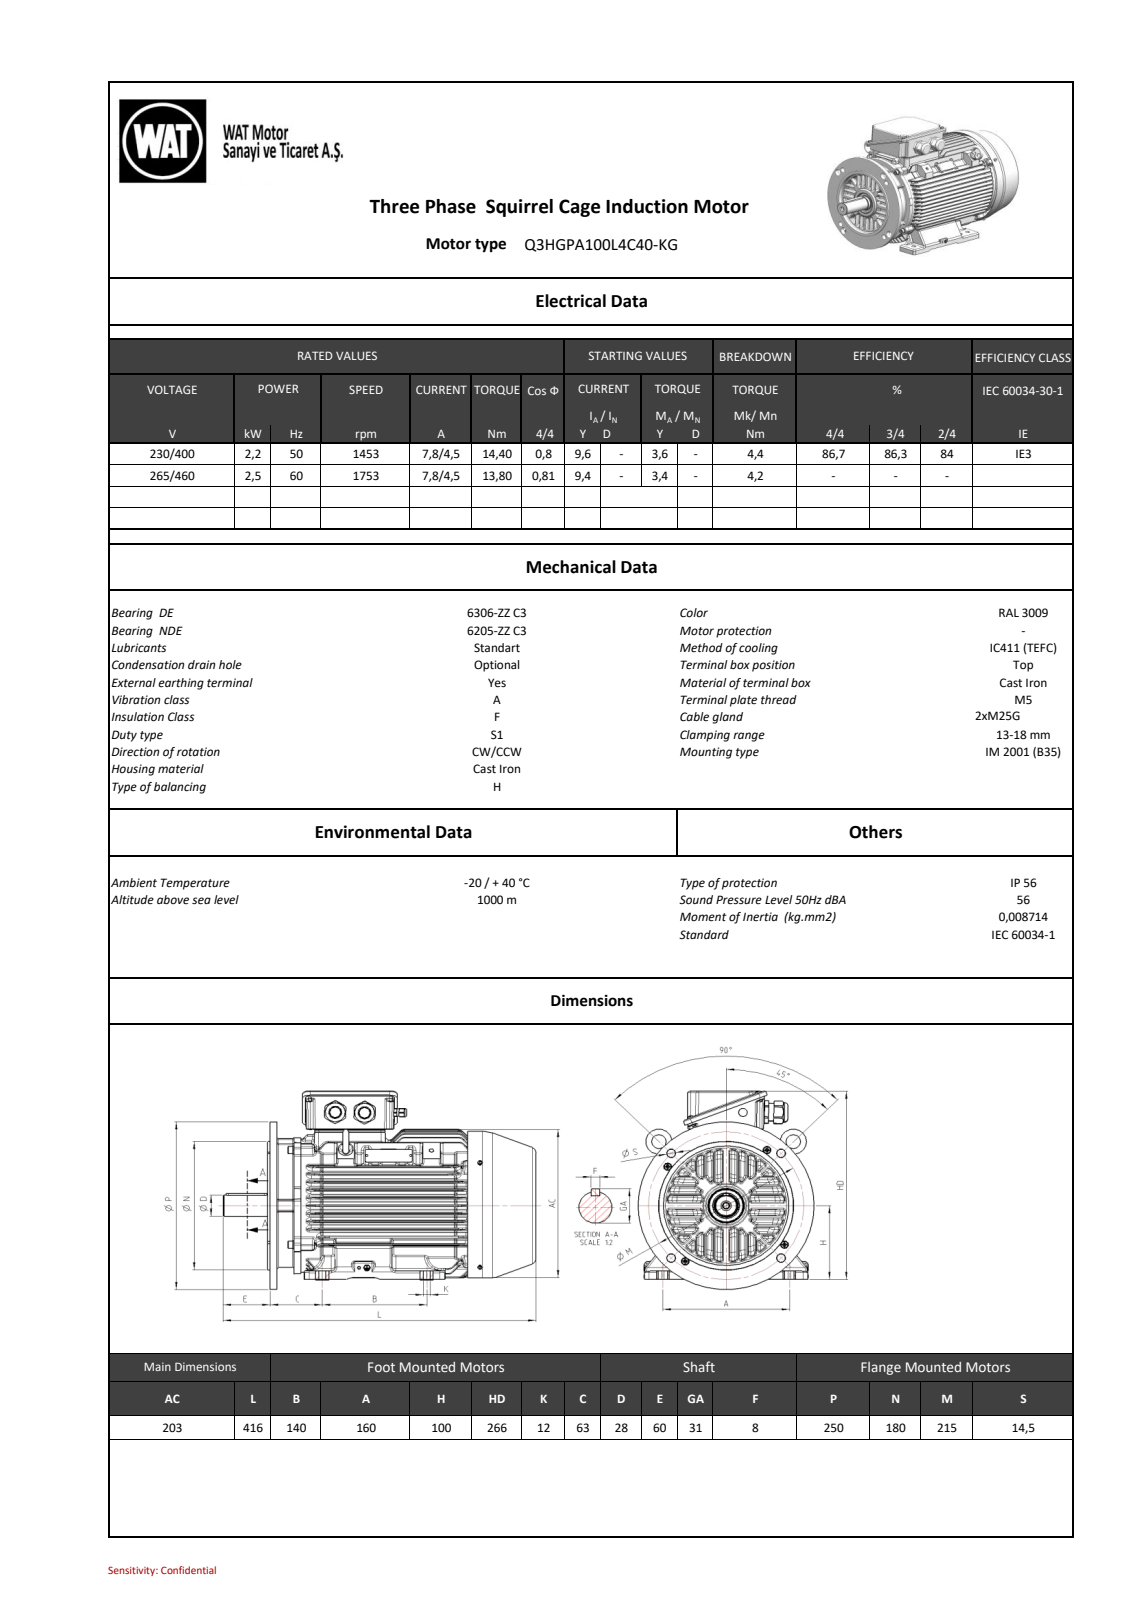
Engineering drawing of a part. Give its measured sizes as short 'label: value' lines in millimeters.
name: 26000A30F4D8roey
written by: SIEMENS PLM Software NX 11.0 (AUTOMOTIVE_DESIGN)
unit: mm
bodies: 0 solids, 4572 faces (884 planar, 1241 cylindrical, 2447 other)
size: 416 × 290.48 × 250
holes: 7× ⌀5, 4× ⌀10, 4× ⌀11, 2× ⌀6.8, 2× ⌀17.2, 1× ⌀4.2, 1× ⌀6.5, 1× ⌀7, 1× ⌀8.5, 1× ⌀10.5, 1× ⌀14, 1× ⌀43.4
bosses: 4× ⌀10, 4× ⌀8.65, 4× ⌀8, 3× ⌀4, 2× ⌀27.7, 2× ⌀25.25, 2× ⌀20, 1× ⌀250
rounds: 370× R3, 141× R1.5, 48× R2, 23× R1.8, 21× R1, 17× R0.25, 12× R26.5, 12× R34.5
face distances: 13.52, 13.61, 27.13, 78.72, 3.2, 51.59, 65.11, 40.83, 27.31, 13.7
hole spacings: 89.5, 126.57, 31.07, 102.68, 146.62, 176.28, 179, 44.5
